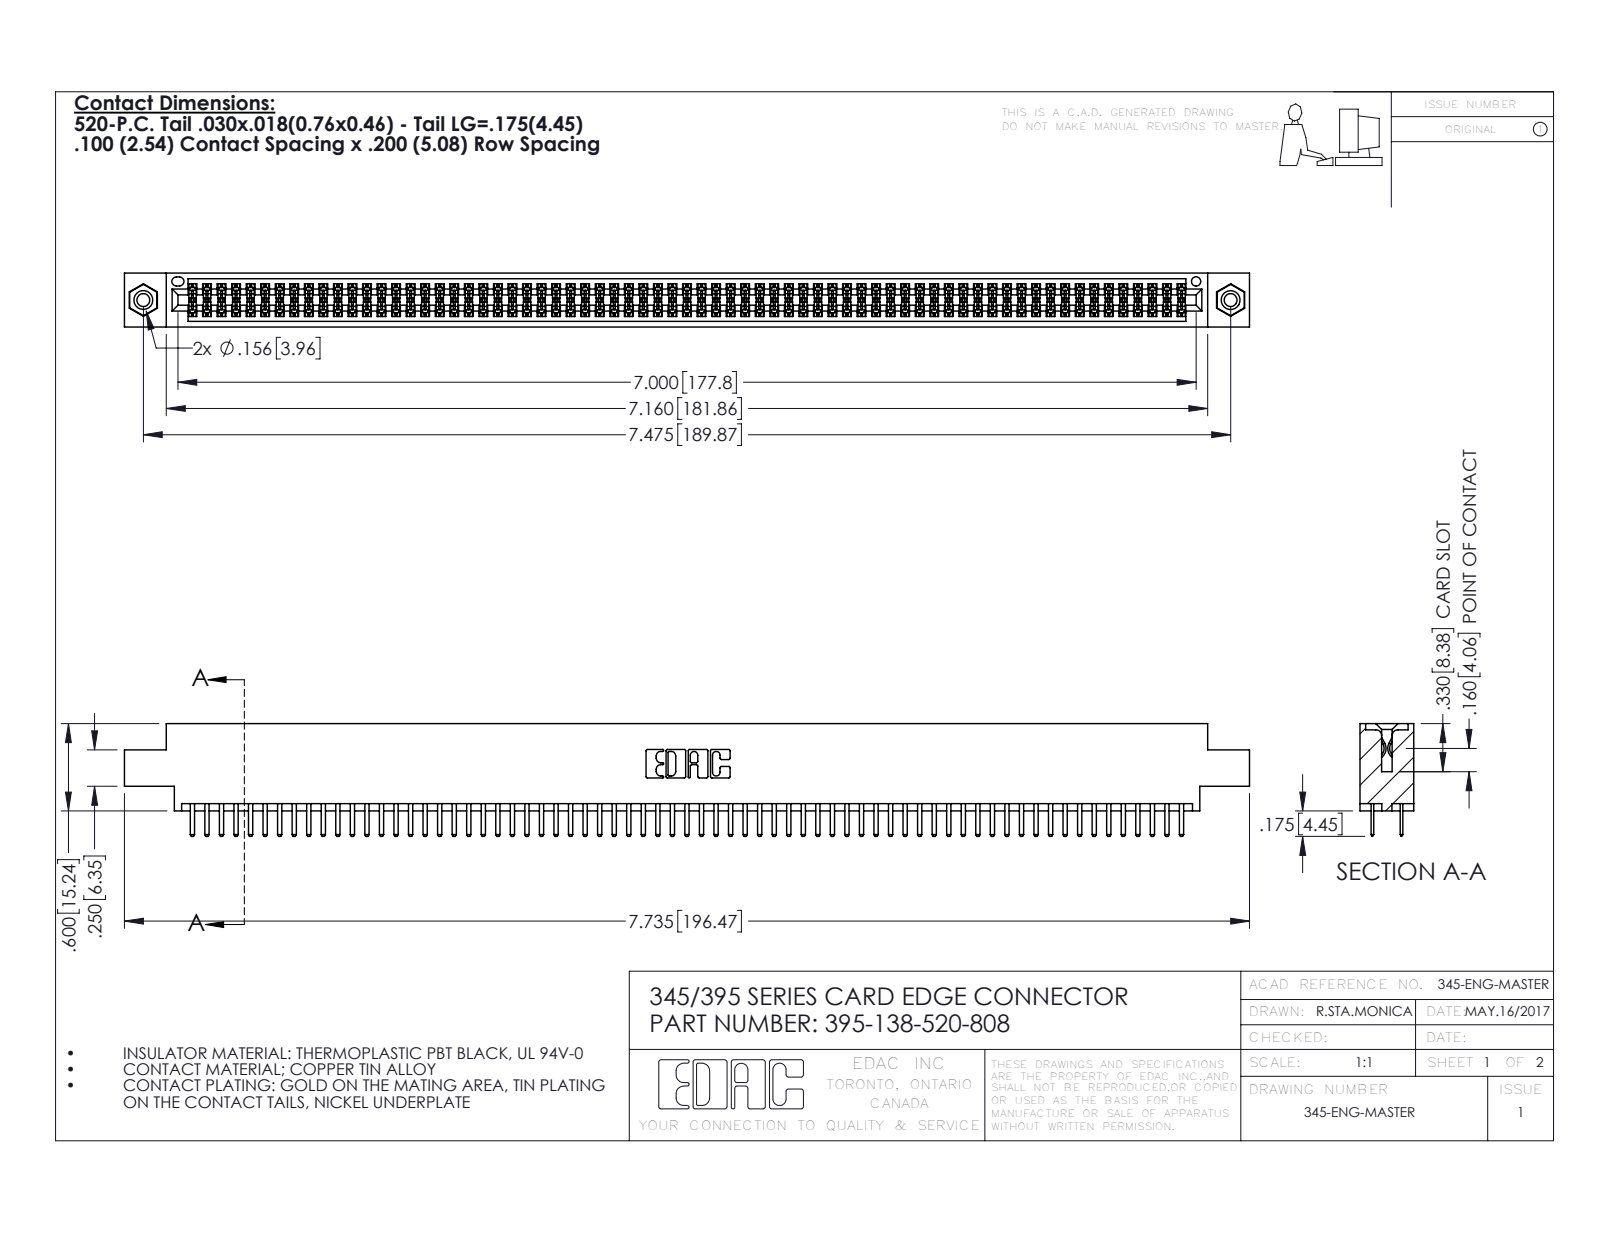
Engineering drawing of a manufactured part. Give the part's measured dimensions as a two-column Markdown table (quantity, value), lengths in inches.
| quantity | value |
| --- | --- |
| part name | 395-138-520-808; 345-250-001_345-250-003-102; 345 Part_0.170 Offset - 0.156 Dia-TI; 345-292-001_345-293-120 |
| STEP written by | SolidWorks 2016 (CONFIG_CONTROL_DESIGN) |
| units | inches |
| bodies | 141 solids, 7642 faces (4946 planar, 2680 cylindrical, 16 other) |
| overall size | 7.735 × 0.775 × 0.37 |
| volume | 1.169 in³ |
| surface area | 44.74 in² |
| round holes (diameter × count) | 0.089 × 2, 0.125 × 2, 0.156 × 2, 0.064 × 1 |
| round bosses / shafts (diameter × count) | 0.155 × 2 |
| partial cylindrical surfaces (radius × count) | 0.006 × 207, 0.01 × 142, 0.01 × 22, 0.007 × 6, 0.031 × 6, 0.026 × 3, 0.014 × 2, 0.019 × 2 |
| main face-to-face distances | 0.072, 0.298, 0.2, 0.37, 0.098, 0.272, 0.025, 0.225, 0.022, 0.072 |
| hole center spacings | 0.27, 7.239, 7.475 |
